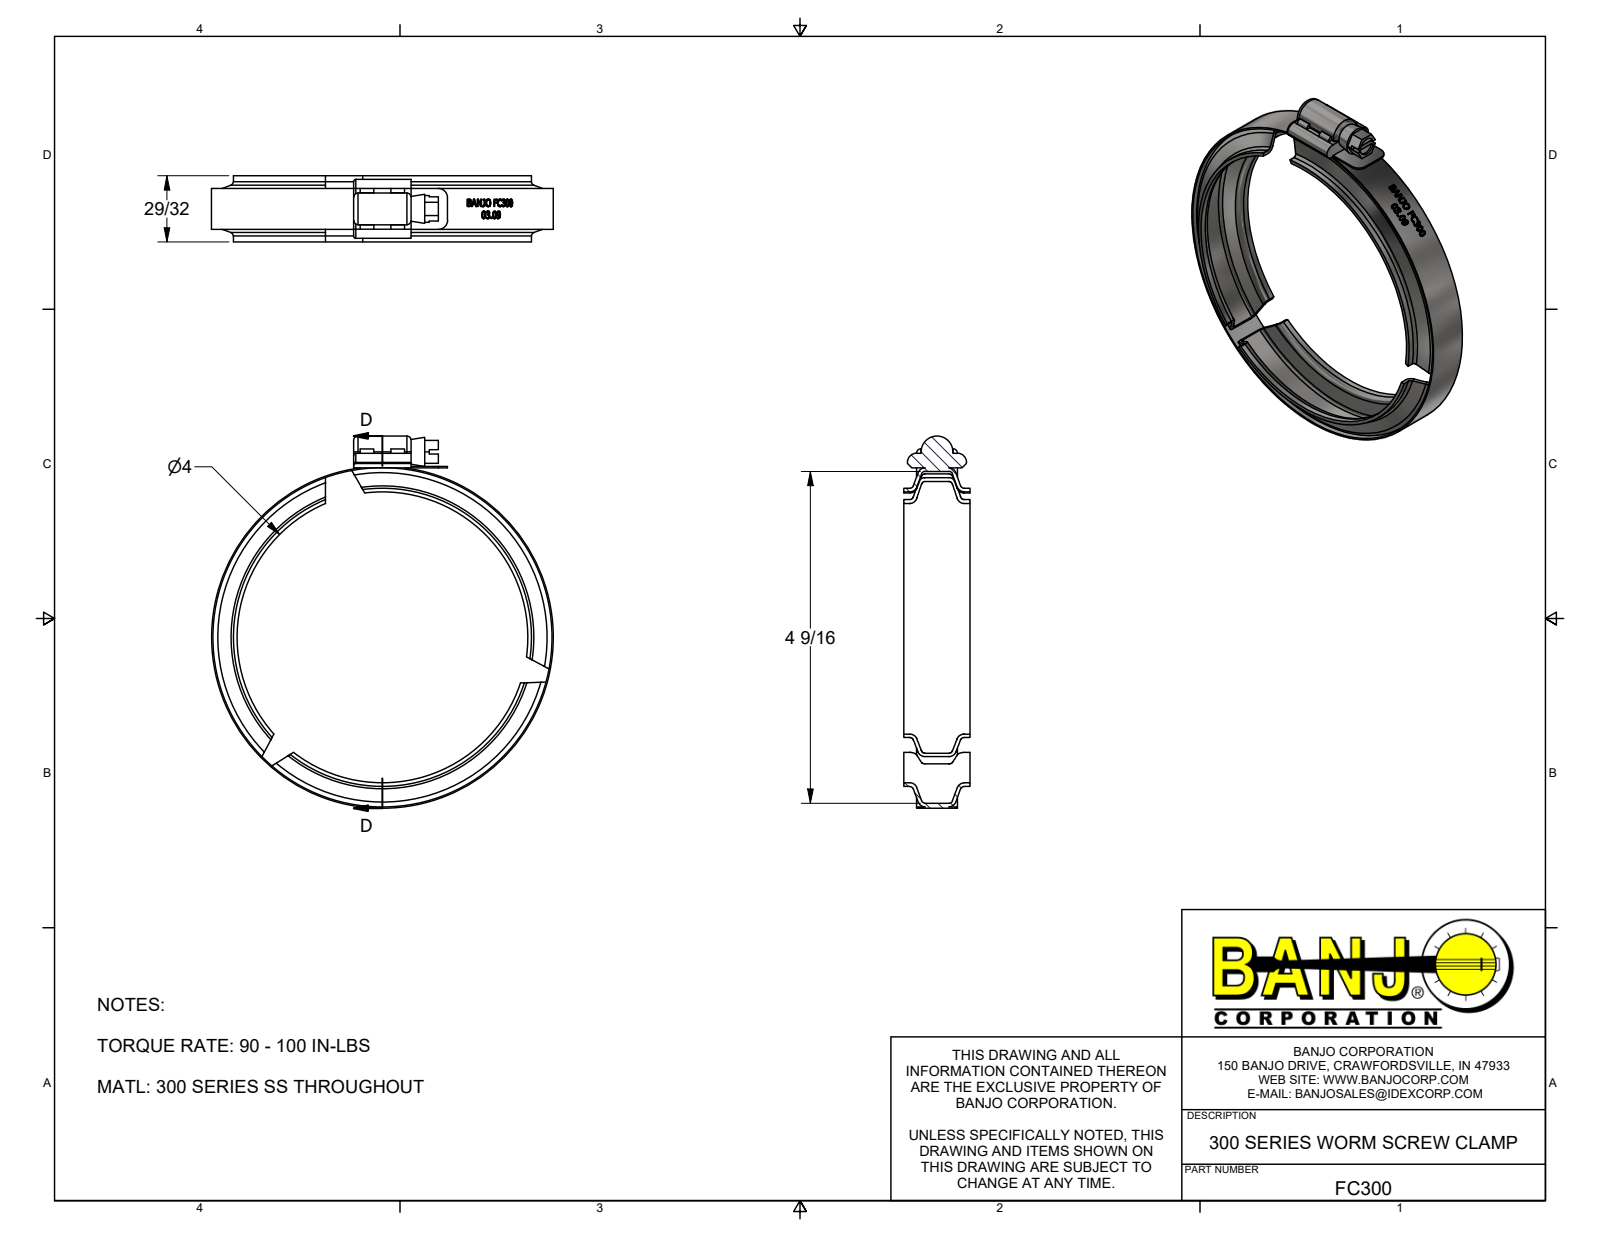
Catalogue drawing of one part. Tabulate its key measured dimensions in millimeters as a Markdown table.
| quantity | value |
| --- | --- |
| part name | FC300 |
| STEP written by | Autodesk Inventor 2018 (AUTOMOTIVE_DESIGN) |
| units | millimeters |
| bodies | 1 solid, 396 faces (133 planar, 58 cylindrical, 205 other) |
| overall size | 130 × 119.4 × 23.1 |
| volume | 19 300 mm³ |
| surface area | 28 360 mm² |
| round holes (diameter × count) | 6.4 × 1, 101.5 × 1, 115.8 × 1, 118.4 × 1 |
| round bosses / shafts (diameter × count) | 119.4 × 1, 104.1 × 1 |
| partial cylindrical surfaces (radius × count) | 1.5 × 4, 3.2 × 4, 0.8 × 3, 5.6 × 1, 59.4 × 1 |
| main face-to-face distances | 4.4, 18.7, 23.1, 14.3, 0.5, 20.1, 8.1, 29.9, 9.8, 4.8 |
